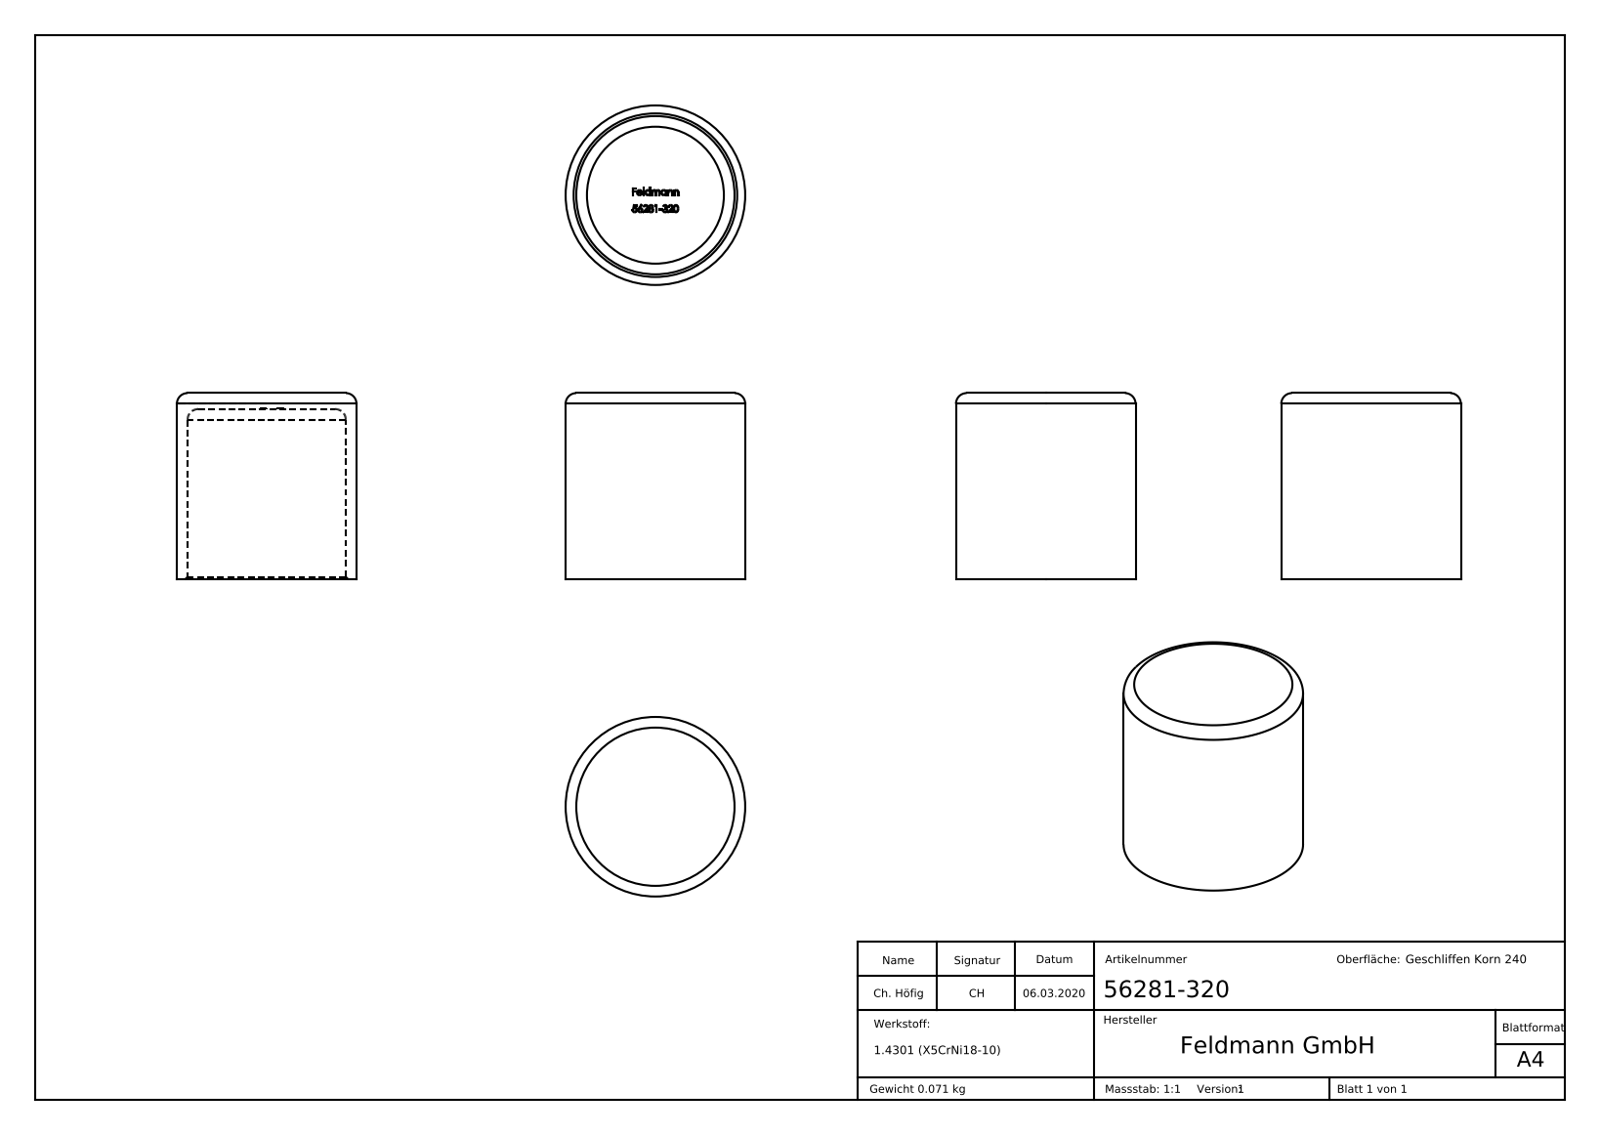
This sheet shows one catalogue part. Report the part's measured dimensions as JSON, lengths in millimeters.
{"part_name": "56281-320", "step_written_by": "SolidWorks 2015 (CONFIG_CONTROL_DESIGN)", "units": "millimeters", "bodies": {"solids": 1, "faces": 237, "planar": 115, "cylindrical": 2, "other": 120}, "overall_size": [35, 33.7, 33.7], "volume_mm3": 9026, "surface_area_mm2": 8283, "round_holes": [[29.7, 1]], "round_bosses_or_shafts": [[33.7, 1]], "face_to_face_distances": [3, 32, 35, 32.1, 2.9, 2.97, 0.39, 3.05, 1.12, 3.39]}
